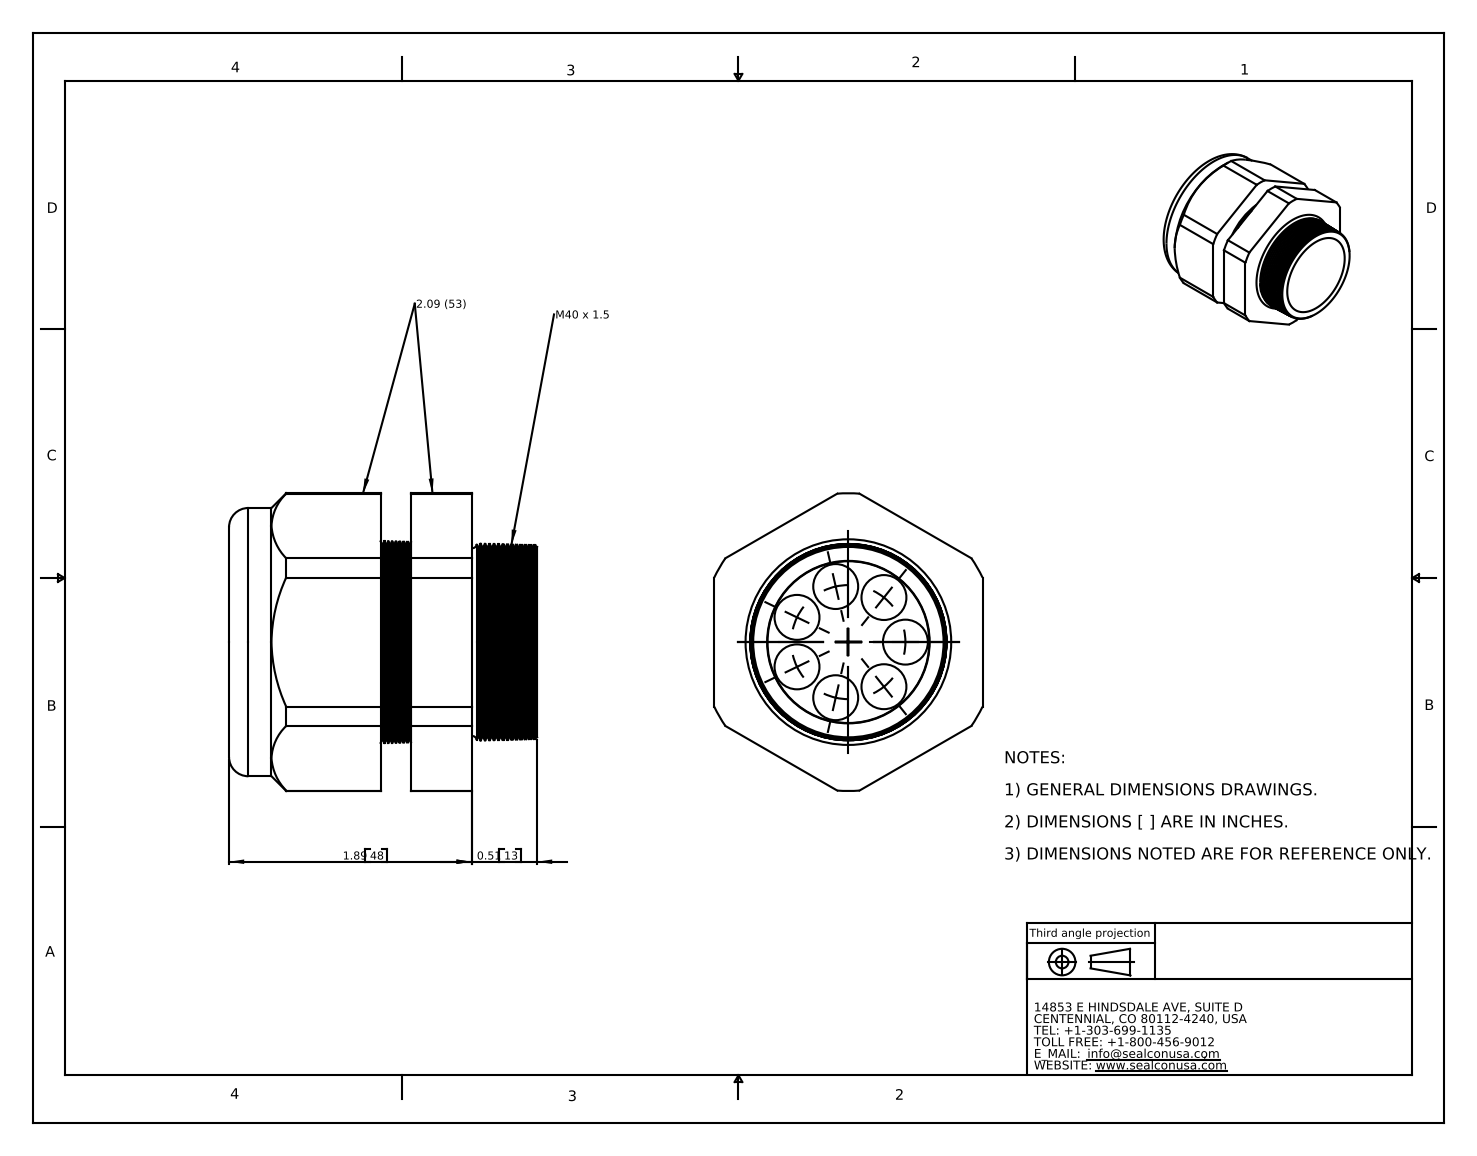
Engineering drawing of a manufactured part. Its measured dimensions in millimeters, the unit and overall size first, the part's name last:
Units: millimetres
Overall size (bounding box): 61 × 58.9 × 53.1
Round holes (diameter × count): ⌀8.9 ×7, ⌀31.5 ×1, ⌀32 ×1
Round bosses / shafts (diameter × count): ⌀53.1 ×1
Partial cylindrical surfaces — rounded edges, fillets, slot ends (radius × count): R29.5 ×1
Main face-to-face distances: 53.1, 6, 18, 12, 30, 36, 48, 12.7, 17.3, 23.3
Hole centre spacings: 17.7, 11.3, 9.8, 22, 9.8, 22, 11.3, 17.6
Volume: 76 580 mm³ · Surface area: 27 430 mm²
Bodies: 2 solids, 203 faces (21 planar, 34 cylindrical, 148 other)
Part name (STEP PRODUCT): CD40M2-GY
STEP written by: SolidWorks 2007 (CONFIG_CONTROL_DESIGN)
